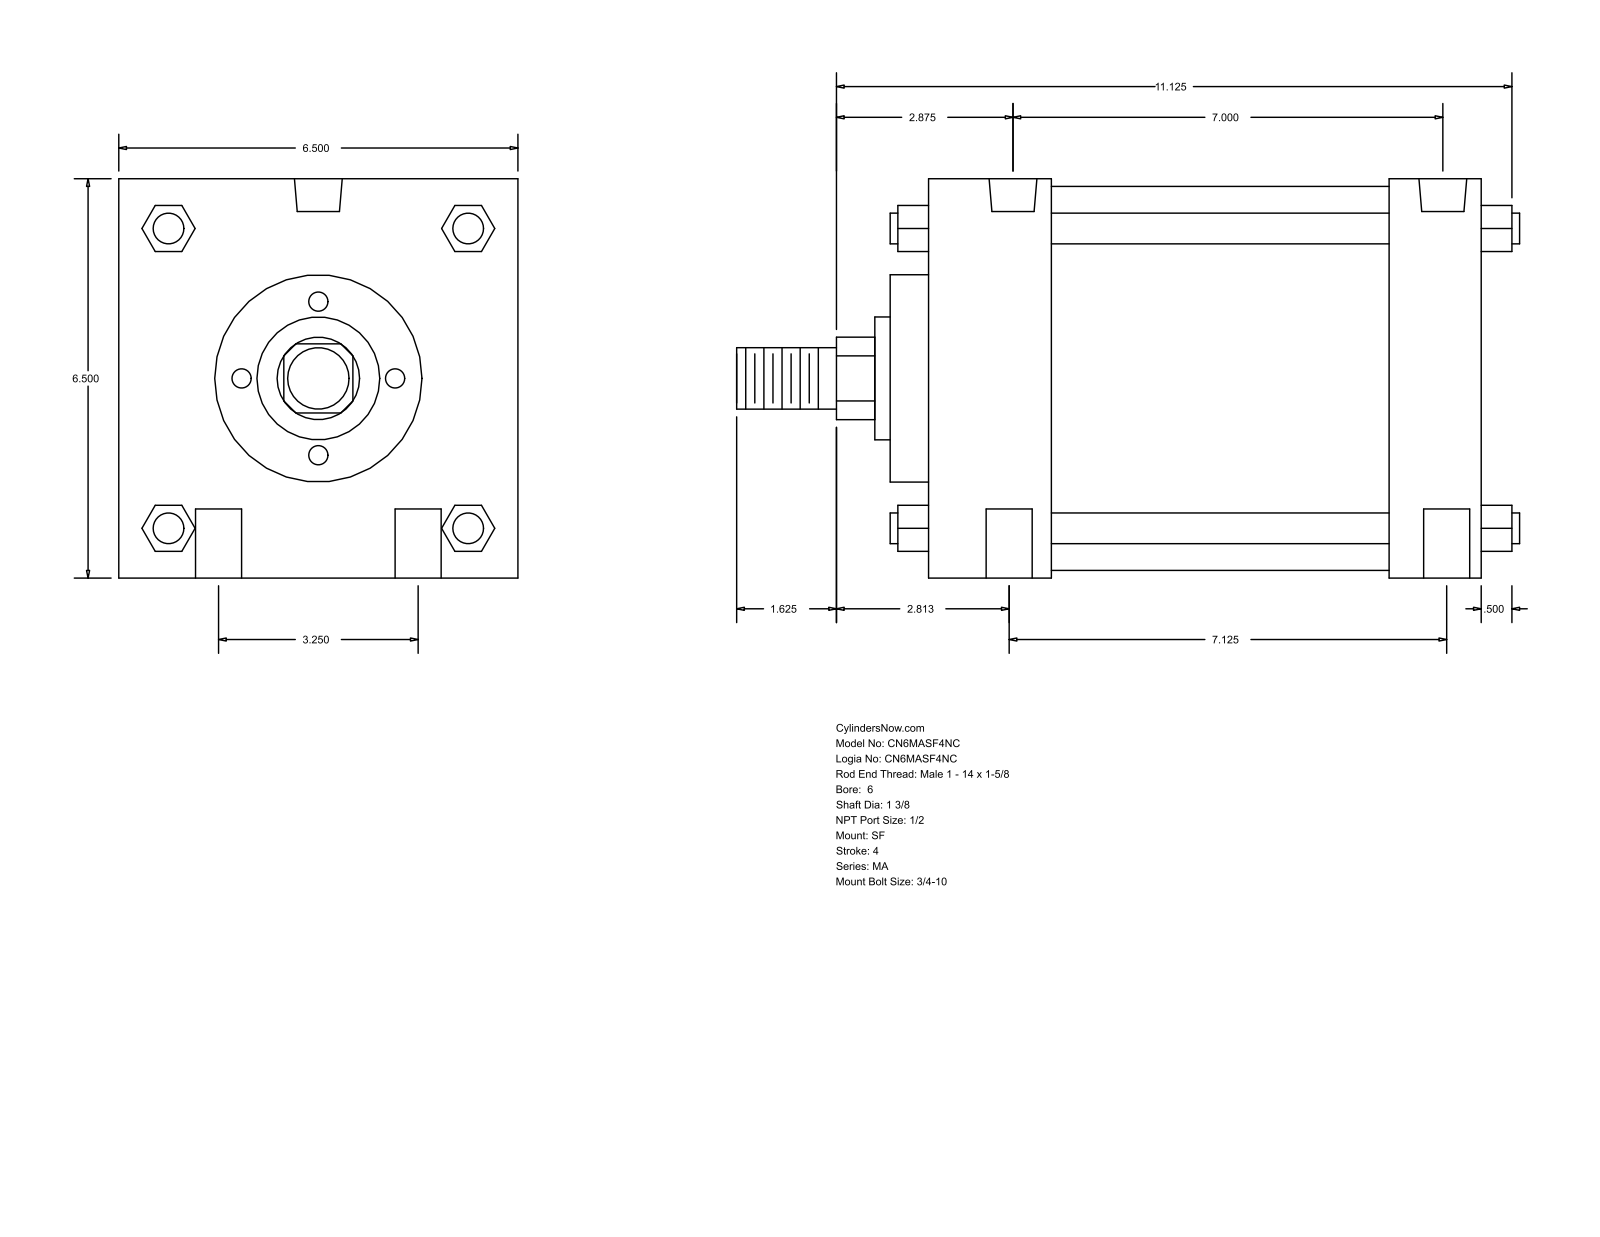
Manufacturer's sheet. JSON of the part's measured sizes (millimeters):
{"part_name": "MA_SF__0600_1.375", "step_written_by": "GSSL Pune (CONFIG_CONTROL_DESIGN)", "units": "millimeters", "bodies": {"solids": 0, "faces": 126, "planar": 95, "cylindrical": 31, "other": 0}, "overall_size": [323.85, 165.1, 165.1], "round_holes": [[19.05, 4], [17.46, 2], [19.77, 2]], "round_bosses_or_shafts": [[12.7, 4], [158.75, 1], [85.72, 1], [50.8, 1], [34.92, 1], [25.4, 1]], "partial_cylinders_radius": [[17.06, 1]], "face_to_face_distances": [165.1, 228.6, 190.5, 50.8, 38.1, 139.7, 177.8, 66.67, 15.87, 244.47], "hole_center_spacings": [41.3, 184.07, 82.54, 180.97, 198.9, 177.79, 177.8]}
